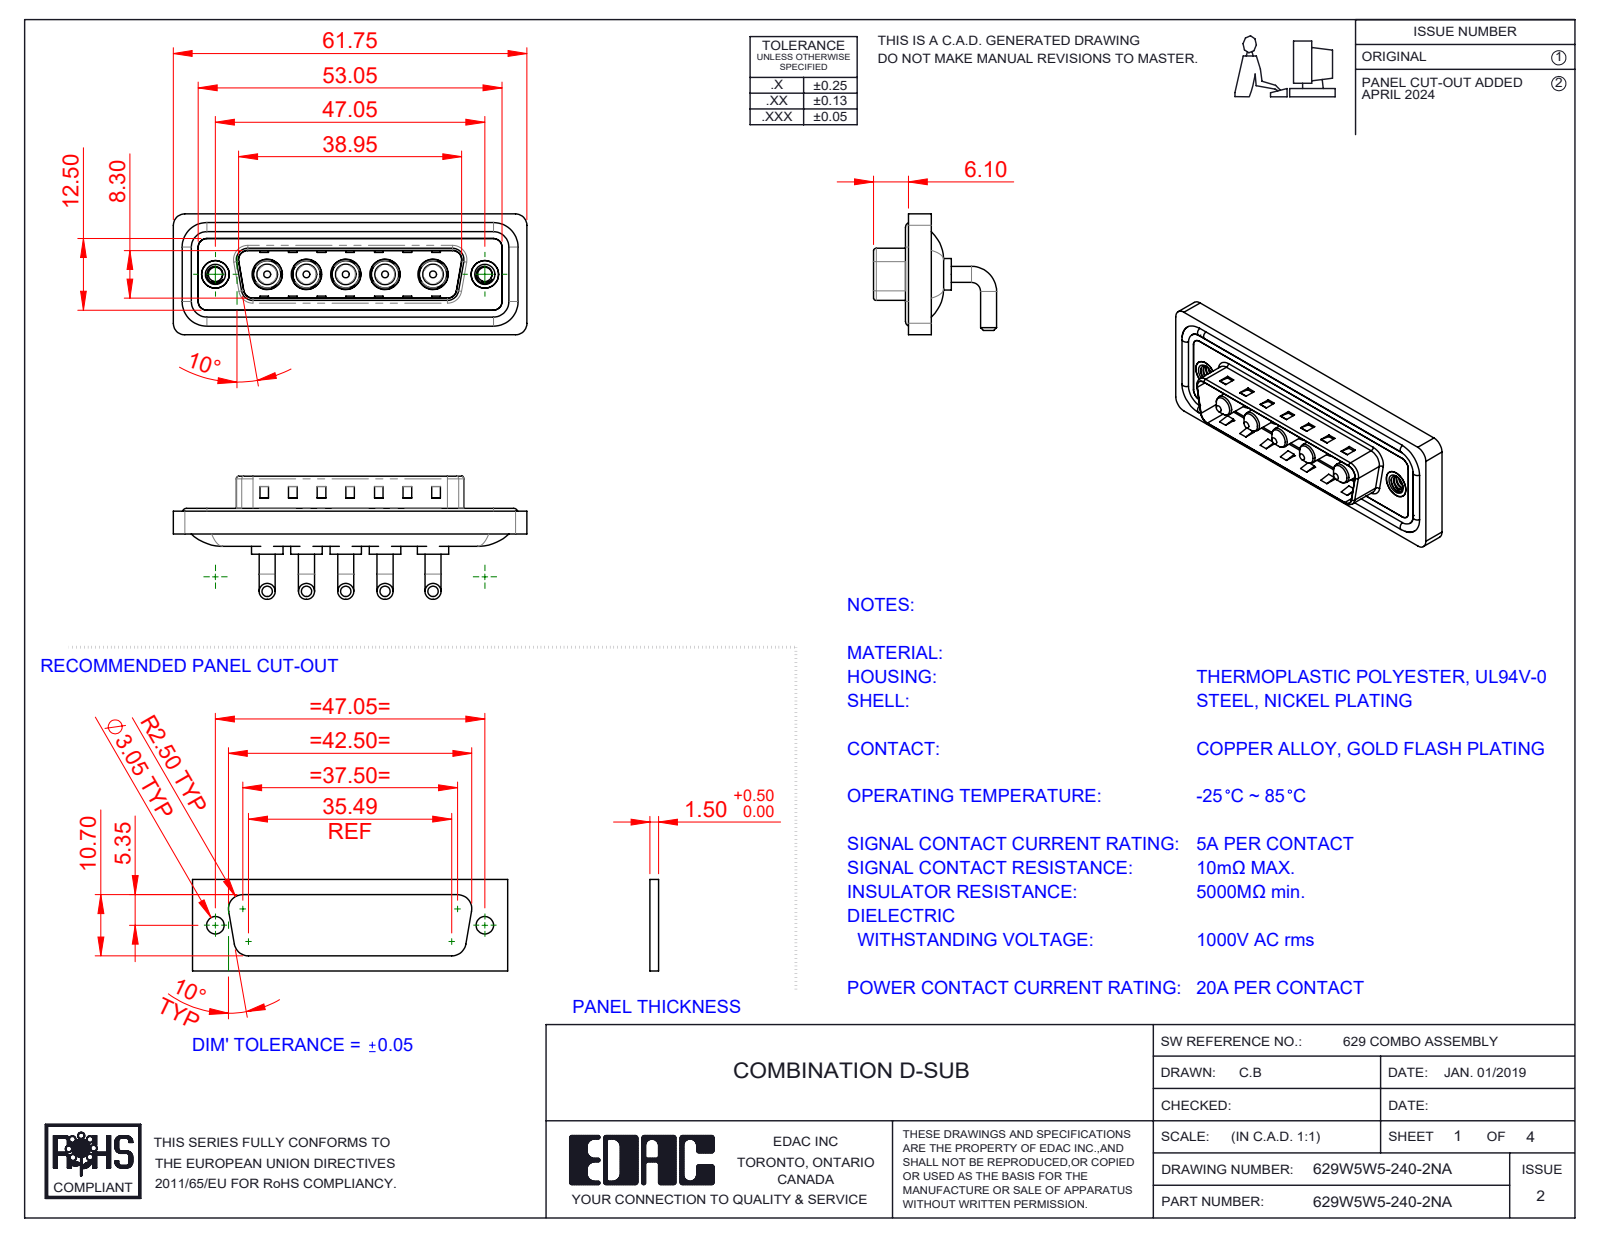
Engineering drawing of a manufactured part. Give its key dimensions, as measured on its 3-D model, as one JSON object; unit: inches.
{"part_name": "629Combo Housing_5W5; Power Pin_20A RA; 629Combo Shell Rear_25 Contacts; 629Combo Waterproof Housing_25 Contacts (+3 more)", "step_written_by": "SolidWorks 2023 (CONFIG_CONTROL_DESIGN)", "units": "inches", "bodies": {"solids": 17, "faces": 692, "planar": 259, "cylindrical": 291, "other": 142}, "overall_size": [2.431, 0.846, 0.831], "volume_in3": 0.476, "surface_area_in2": 19.03, "round_holes": [[0.191, 5], [0.209, 5], [0.098, 2], [0.157, 2], [0.189, 2], [0.197, 2]], "round_bosses_or_shafts": [[0.11, 10], [0.217, 5], [0.205, 5], [0.187, 5], [0.148, 5], [0.142, 5], [0.063, 4], [0.193, 2]], "partial_cylinders_radius": [[0.059, 18], [0.079, 18], [0.02, 8], [0.063, 8], [0.083, 5], [0.01, 4], [0.024, 4], [0.026, 4]], "face_to_face_distances": [0.016, 0.114, 0.031, 0.177, 0.161, 0.043, 0.083, 0.122, 0.059, 0.236], "hole_center_spacings": [0.27, 0.541, 0.27, 0.27, 0.33, 0.33, 0.356, 0.356]}
